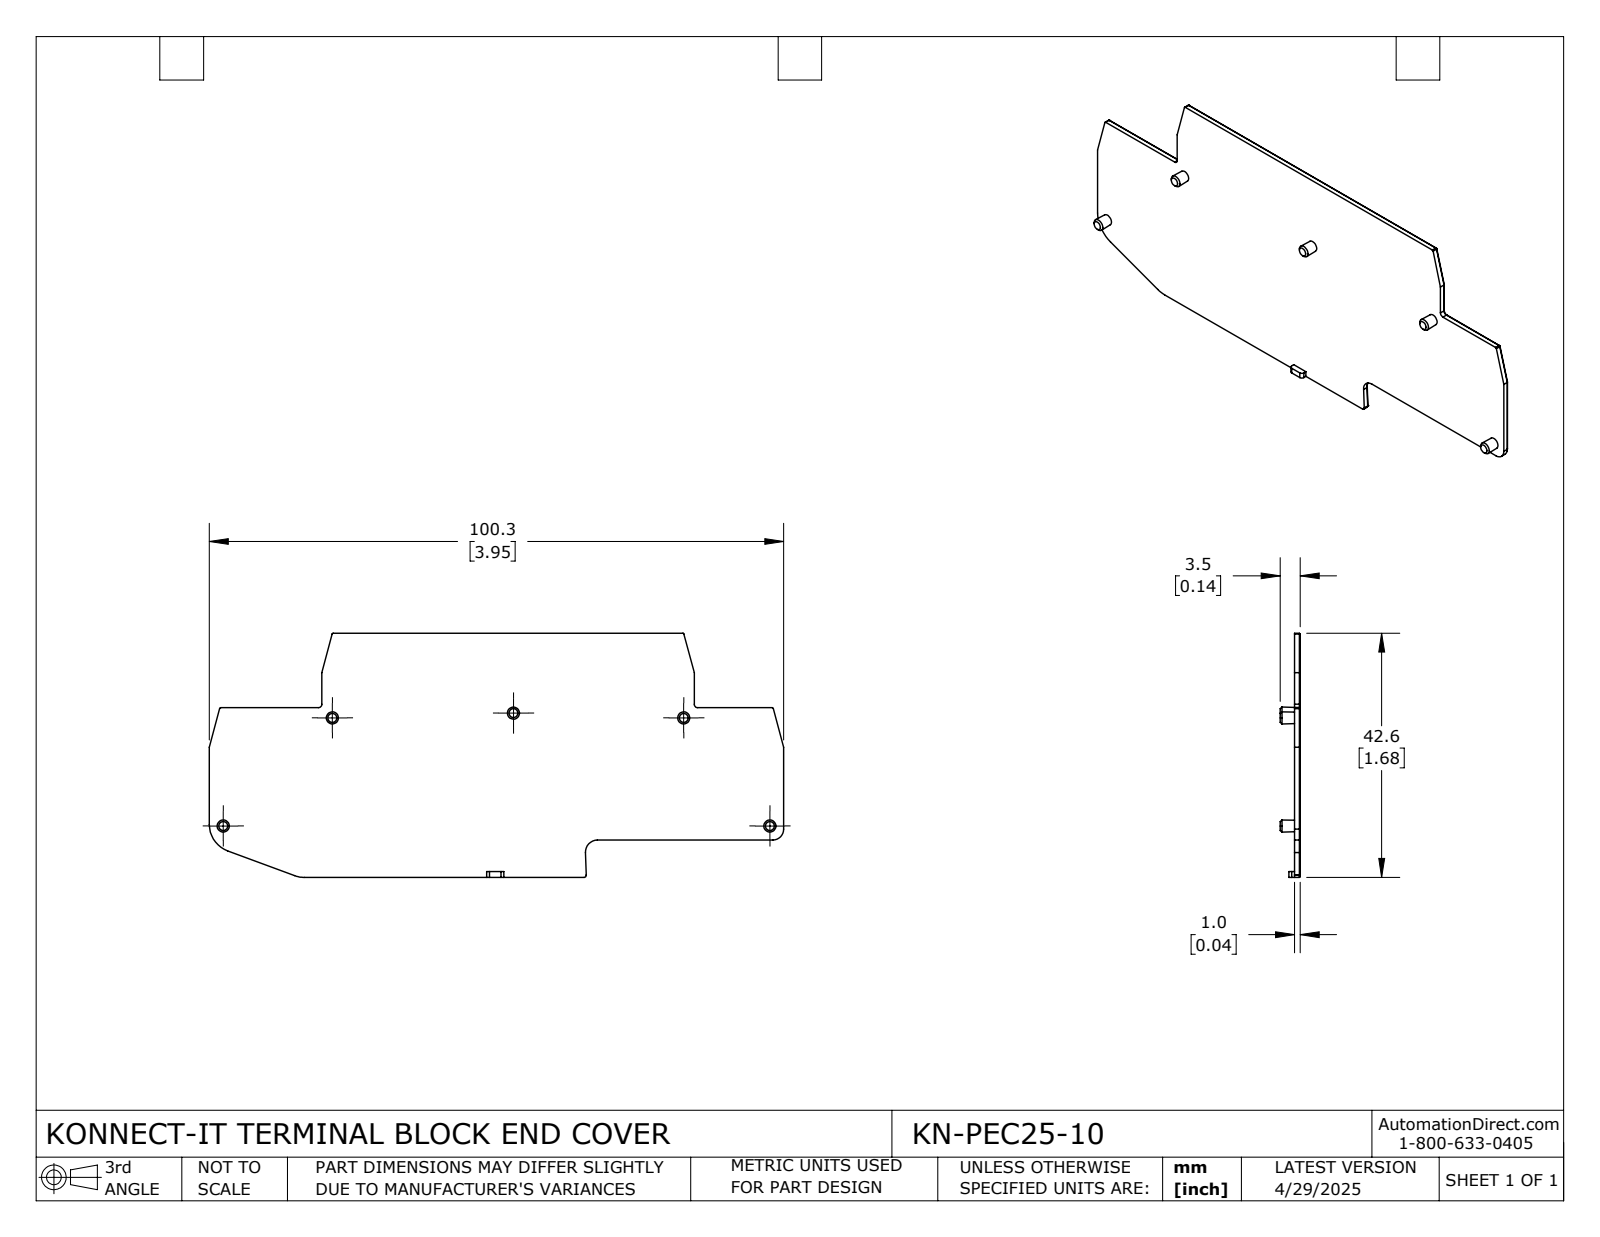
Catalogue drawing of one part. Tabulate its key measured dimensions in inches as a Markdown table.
| quantity | value |
| --- | --- |
| part name | KN-PEC25-10 |
| STEP written by | SolidWorks 2024 (CONFIG_CONTROL_DESIGN) |
| units | inches |
| bodies | 1 solid, 92 faces (44 planar, 28 cylindrical, 20 other) |
| overall size | 3.949 × 1.678 × 0.138 |
| volume | 0.217 in³ |
| surface area | 11.46 in² |
| partial cylindrical surfaces (radius × count) | 0.004 × 4, 0.008 × 4, 0.02 × 2, 0.024 × 2, 0.028 × 2, 0.189 × 2, 0.193 × 2, 0.012 × 1 |
| main face-to-face distances | 0.039, 1.678, 0.256, 0.512, 0.033, 1.422, 1.166, 0.909, 1.674, 1.418 |
